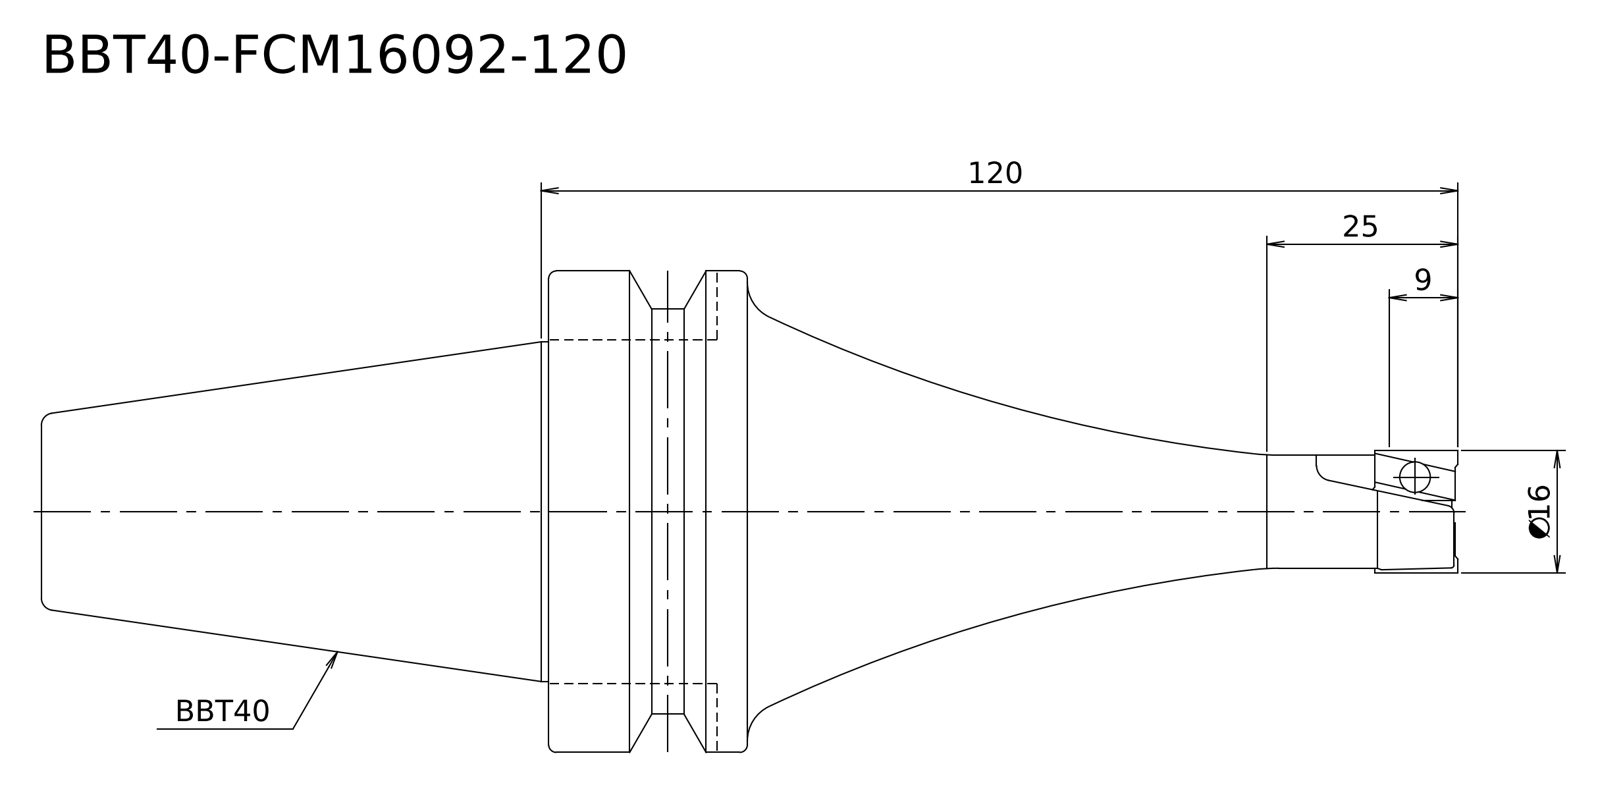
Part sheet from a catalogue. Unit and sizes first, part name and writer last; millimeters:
Units: millimetres
Overall size (bounding box): 185.4 × 63 × 63
Round bosses / shafts (diameter × count): ⌀63 ×1, ⌀53 ×1, ⌀44.45 ×1, ⌀16 ×1, ⌀14.8 ×1
Main face-to-face distances: 66.4, 26, 92.4, 93, 119, 185.4
Volume: 211 807 mm³ · Surface area: 24 989 mm²
Bodies: 1 solid, 17 faces (4 planar, 6 cylindrical, 7 other)
STEP written by: Kubotek KeyCreator V8.5.1 (14335) (CONFIG_CONTROL_DESIGN)
